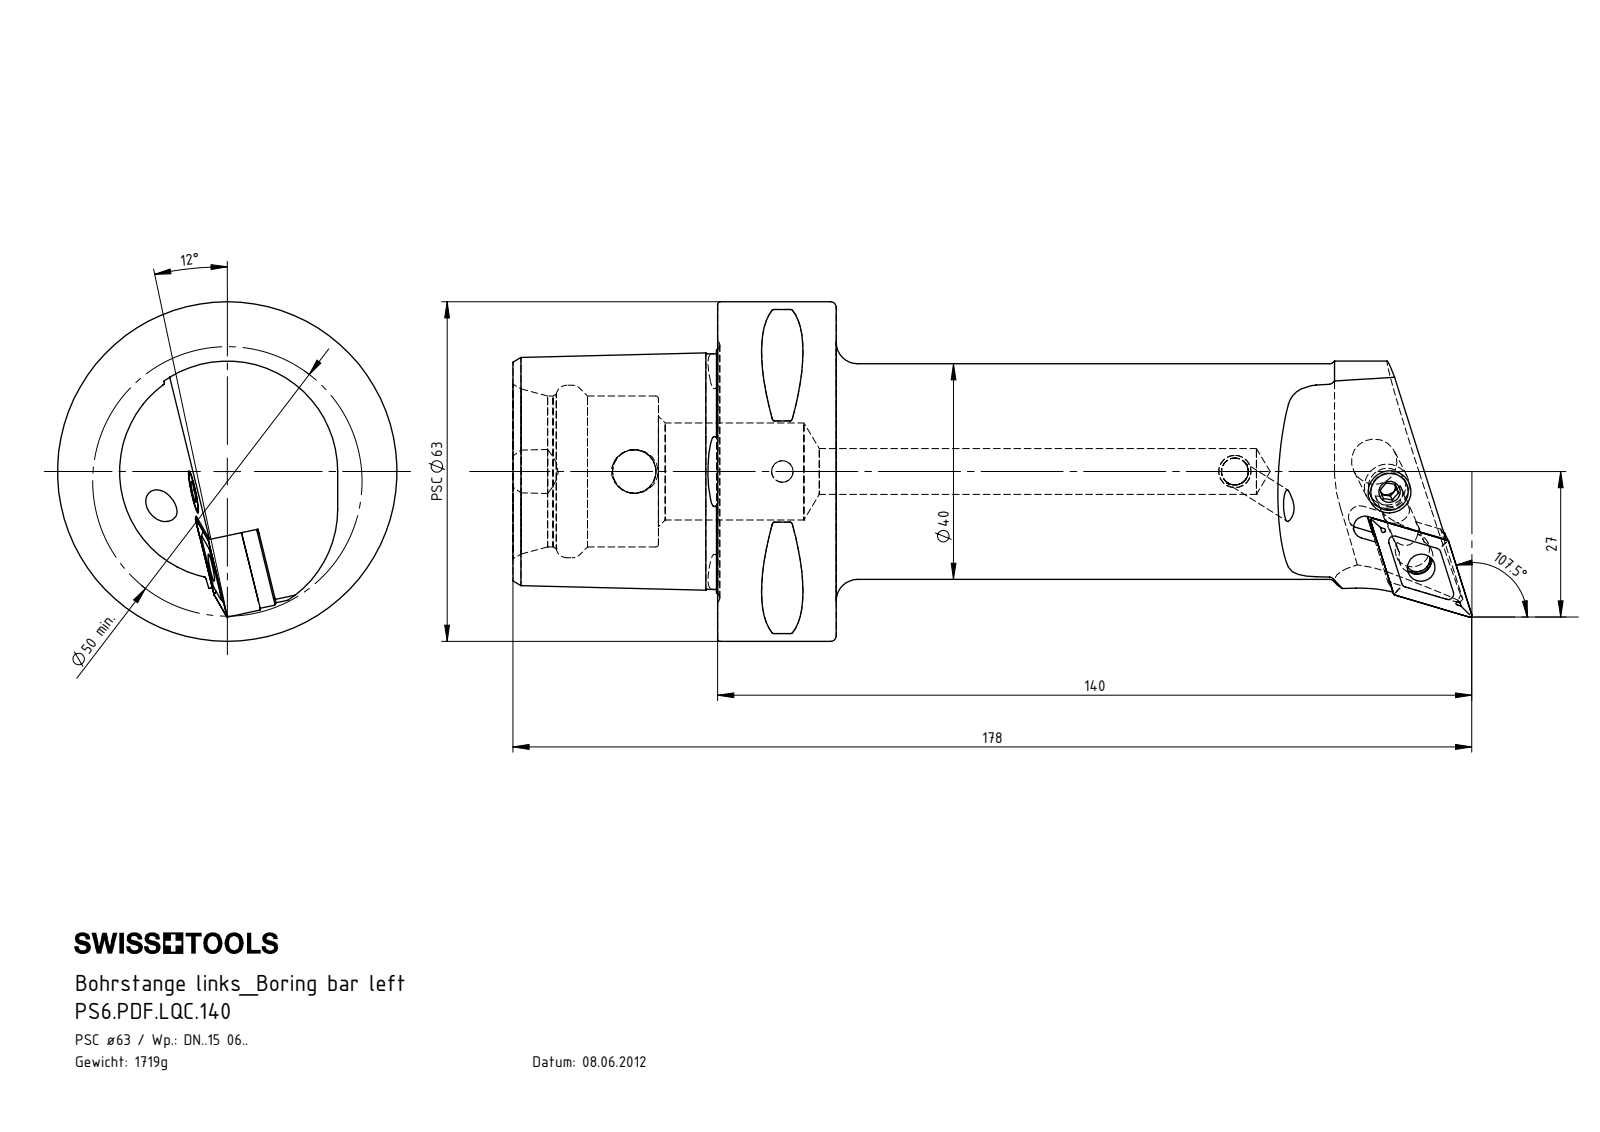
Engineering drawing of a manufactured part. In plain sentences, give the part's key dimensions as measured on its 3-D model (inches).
The part is named "DNMG150604; WCD-ER4.101.017_A; KVT_MB_600_060; PS6.PDF.LQC.140 (+4 more)". Its 3-D file was written by "SolidWorks 2017 (AUTOMOTIVE_DESIGN)". It is 8 solids with 352 faces: 92 planar, 87 cylindrical and 173 other. Overall it measures 7.008 by 2.48 by 2.48 inches. Its volume is 13.42 cubic inches and its surface area 61.97 square inches. Round holes: 1 of diameter 0.157, 1 of diameter 0.165, 1 of diameter 0.197, 1 of diameter 0.203, 1 of diameter 0.252, 1 of diameter 0.276, 1 of diameter 0.319, 1 of diameter 0.331, 1 of diameter 0.335, 1 of diameter 0.709, 1 of diameter 1.102, 1 of diameter 1.26. Round bosses or shafts: 1 of diameter 2.48, 1 of diameter 1.575, 1 of diameter 0.315, 1 of diameter 0.311, 1 of diameter 0.252, 1 of diameter 0.236, 1 of diameter 0.185, 1 of diameter 0.14. Partial cylindrical surfaces (rounded edges, fillets, slot ends): 8 of radius 0.02, 4 of radius 0.016, 4 of radius 0.039, 2 of radius 0.098, 1 of radius 0.083, 1 of radius 0.093, 1 of radius 0.11, 1 of radius 0.118. The main face-to-face distances are 0.866, 1.496, 2.362, 0.238, 0.98, 1.063, 0.433, 1.299, 0.483, 2.197. The hole center spacings are 0.614, 1.083, 3.307, 4.39.
